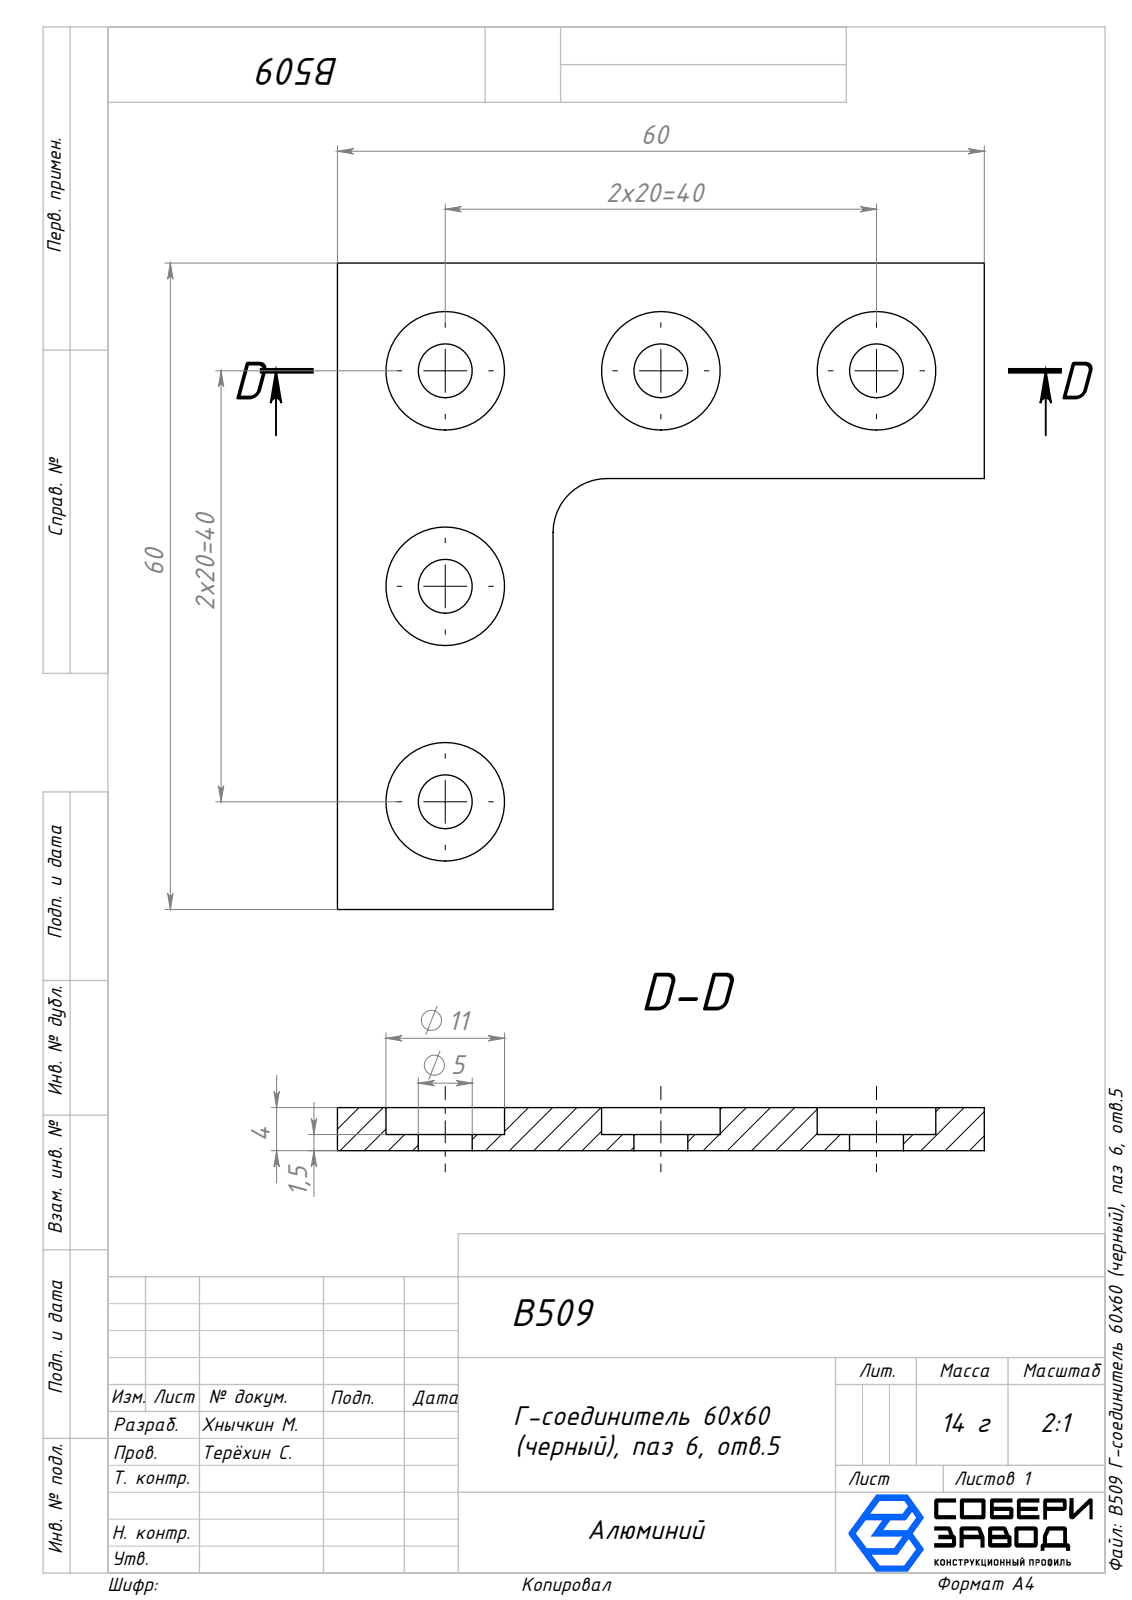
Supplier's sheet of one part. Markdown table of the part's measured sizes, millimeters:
| quantity | value |
| --- | --- |
| part name | B509 Г-соединитель 60х60 (черный), паз 6, отв.5 |
| STEP written by | SolidWorks 2025 (AUTOMOTIVE_DESIGN) |
| units | millimeters |
| bodies | 1 solid, 34 faces (13 planar, 21 cylindrical, 0 other) |
| overall size | 60 × 60 × 4 |
| volume | 6 686 mm³ |
| surface area | 5 316 mm² |
| round holes (diameter × count) | 5 × 5, 11 × 5 |
| partial cylindrical surfaces (radius × count) | 5 × 1 |
| main face-to-face distances | 4, 2.5, 1.5, 20, 60, 40 |
| hole center spacings | 20, 40, 44.72, 28.28, 56.57 |
